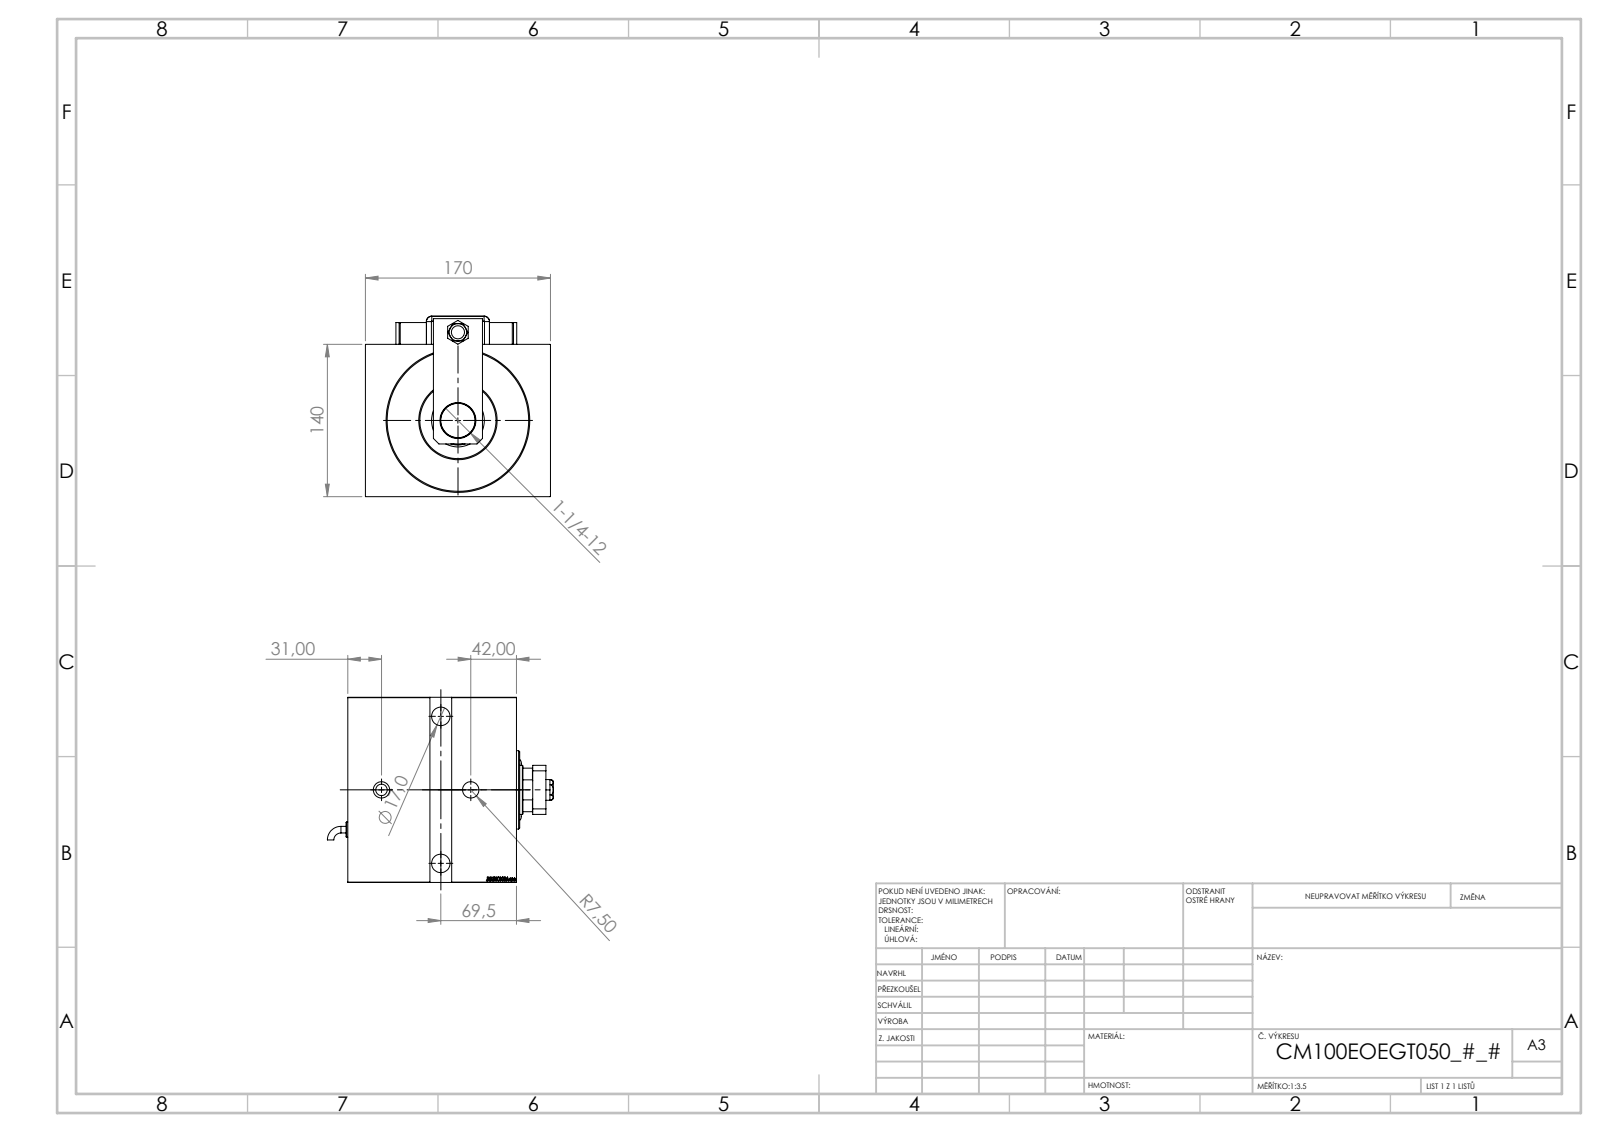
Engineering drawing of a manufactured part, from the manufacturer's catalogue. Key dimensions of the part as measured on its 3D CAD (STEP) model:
Part name (STEP PRODUCT): SWITCH_Q_FRONT_BACK; NUT_D19; MAGNETIC SWITCH Q; V450CM_VC_B (+8 more)
STEP written by: SolidWorks 2019 (CONFIG_CONTROL_DESIGN)
Units: millimetres
Bodies: 13 solids, 1223 faces (613 planar, 93 cylindrical, 517 other)
Overall size (bounding box): 207.66 × 170 × 165.8
Volume: 3 494 000 mm³ · Surface area: 360 476 mm²
Round holes (diameter × count): ⌀4 ×2, ⌀8 ×2, ⌀15 ×2, ⌀17 ×2, ⌀25 ×2, ⌀12 ×1, ⌀13 ×1, ⌀14 ×1, ⌀31.5 ×1, ⌀33 ×1, ⌀45 ×1, ⌀48.5 ×1
Round bosses / shafts (diameter × count): ⌀20 ×3, ⌀16 ×2, ⌀14 ×2, ⌀6 ×2, ⌀102 ×1, ⌀72 ×1, ⌀10.5 ×1
Partial cylindrical surfaces — rounded edges, fillets, slot ends (radius × count): R5 ×9, R10 ×1, R22 ×1
Main face-to-face distances: 170, 155, 140, 26, 129, 3, 5, 150, 124, 20
Hole centre spacings: 37.36, 72.89, 85.67, 86.76, 100.19, 118.42, 20, 81
